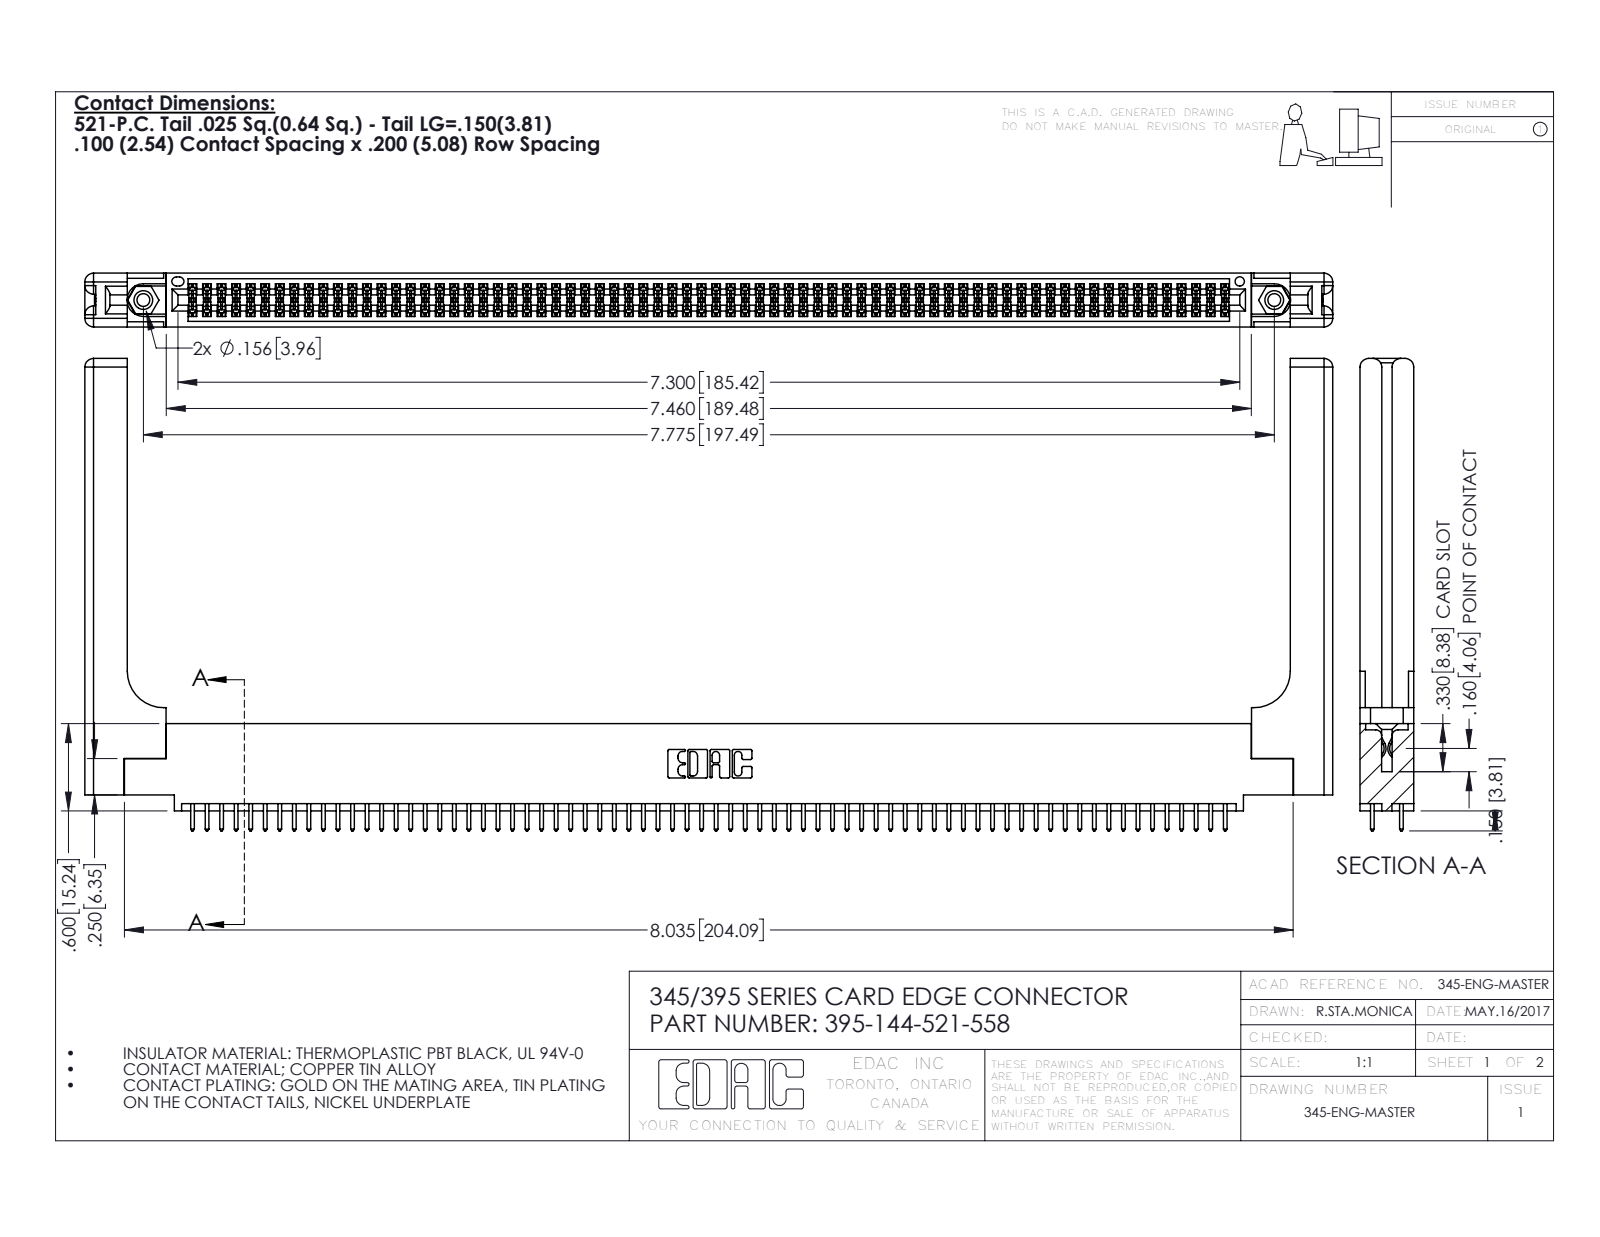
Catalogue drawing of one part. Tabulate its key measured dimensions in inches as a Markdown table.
| quantity | value |
| --- | --- |
| part name | 345-250-001_345-250-001-102; 345-292-001_345-293-121; 395-144-521-558; 345 Part_0.110 Offset - 0.156 Dia-TH (+1 more) |
| STEP written by | SolidWorks 2016 (CONFIG_CONTROL_DESIGN) |
| units | inches |
| bodies | 149 solids, 7586 faces (4984 planar, 2542 cylindrical, 60 other) |
| overall size | 8.579 × 3.247 × 0.37 |
| volume | 1.818 in³ |
| surface area | 57.13 in² |
| round holes (diameter × count) | 0.089 × 2, 0.125 × 2, 0.156 × 2, 0.064 × 1 |
| round bosses / shafts (diameter × count) | 0.155 × 2 |
| partial cylindrical surfaces (radius × count) | 0.006 × 216, 0.01 × 144, 0.01 × 22, 0.06 × 16, 0.007 × 6, 0.031 × 6, 0.026 × 3, 0.014 × 2 |
| main face-to-face distances | 0.072, 0.298, 0.37, 0.098, 0.272, 0.025, 0.2, 0.225, 0.175, 0.148 |
| hole center spacings | 0.27, 7.539, 7.775 |
